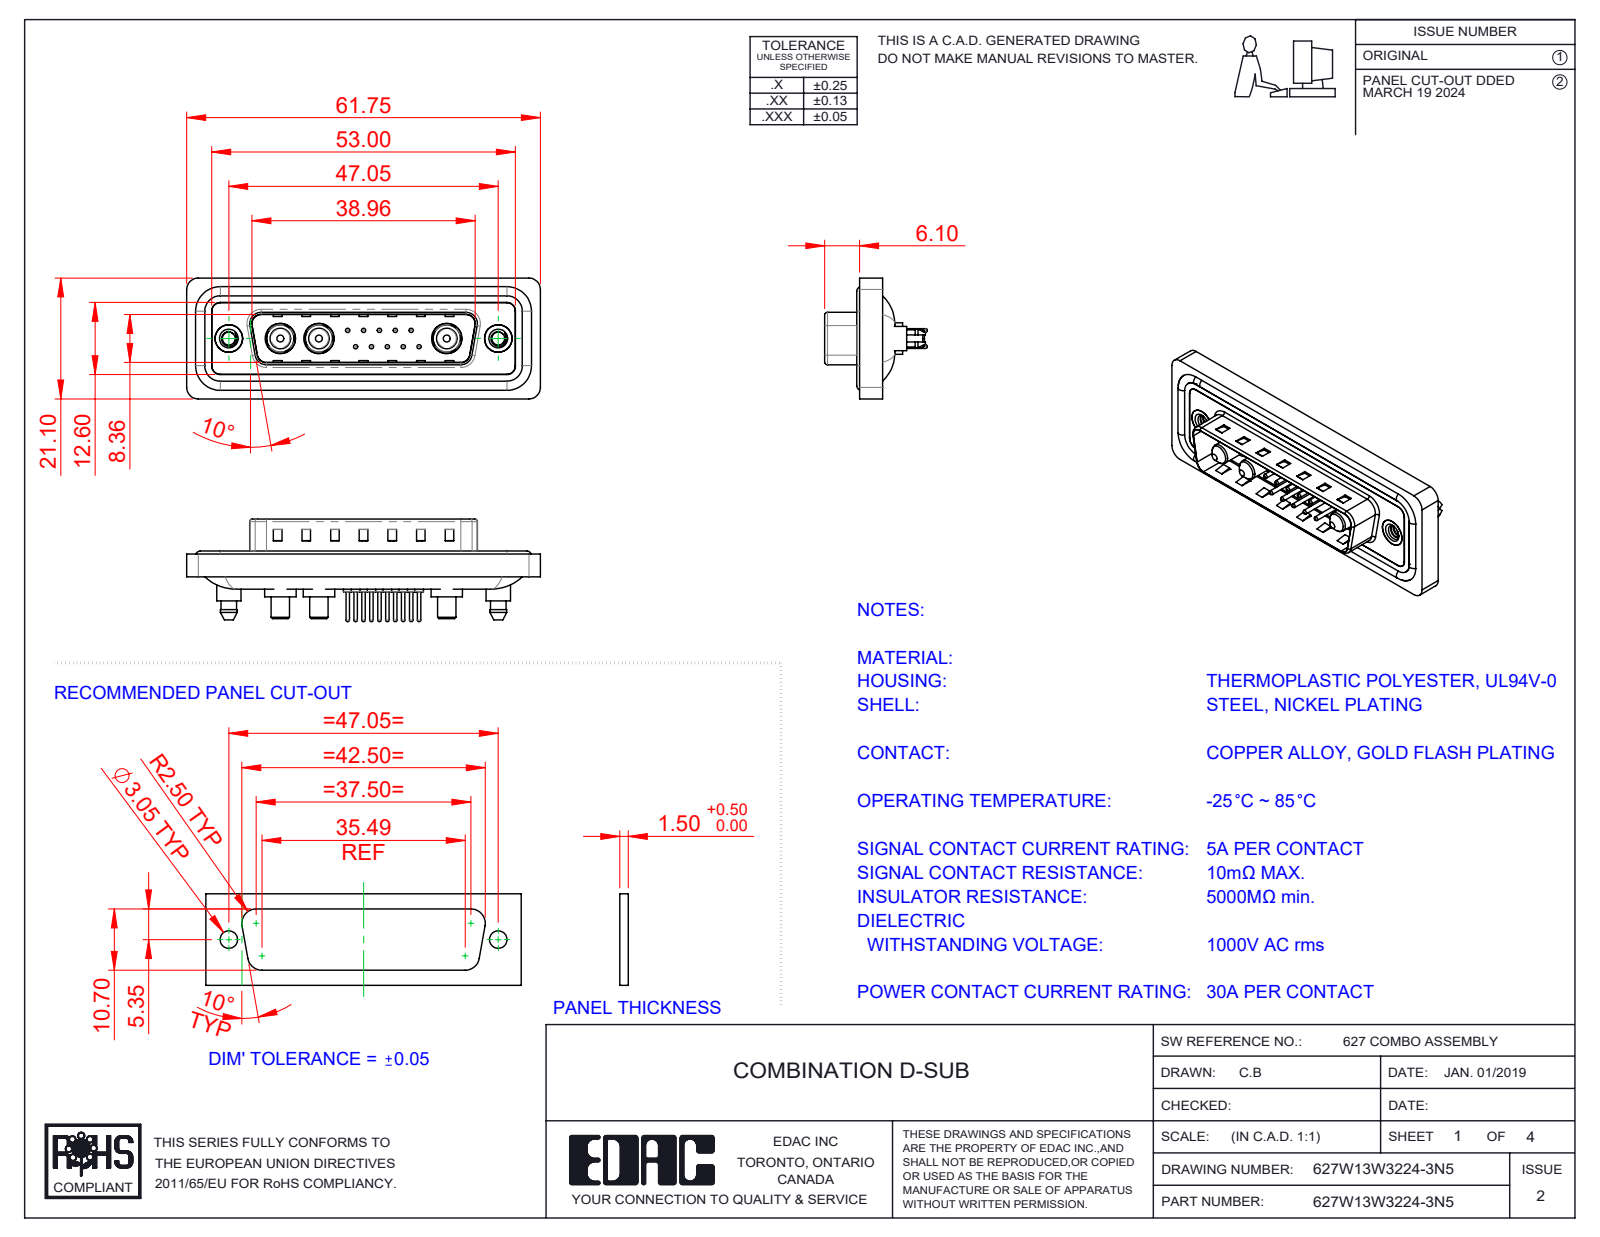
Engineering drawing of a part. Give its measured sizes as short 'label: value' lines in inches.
name: 627Combo Contact Row 2_24; 627Combo Contact Row 1_24; 627Combo Shell Rear_25 Contacts; 627Combo Waterproof Housing_25 Contacts (+5 more)
written by: SolidWorks 2023 (CONFIG_CONTROL_DESIGN)
unit: in
bodies: 23 solids, 1020 faces (325 planar, 417 cylindrical, 278 other)
size: 2.431 × 0.831 × 0.705
volume: 0.457 in³; area: 18.94 in²
holes: 10× ⌀0.03, 10× ⌀0.063, 10× ⌀0.079, 3× ⌀0.191, 3× ⌀0.209, 2× ⌀0.089, 2× ⌀0.157, 2× ⌀0.189, 2× ⌀0.197
bosses: 10× ⌀0.059, 10× ⌀0.024, 4× ⌀0.063, 3× ⌀0.217, 3× ⌀0.205, 3× ⌀0.187, 3× ⌀0.148, 3× ⌀0.142
rounds: 24× R0.059, 18× R0.079, 10× R0.063, 8× R0.02, 4× R0.01, 4× R0.024, 4× R0.026, 4× R0.035
face distances: 0.016, 0.059, 0.043, 0.063, 0.02, 0.122, 0.114, 0.032, 0.377, 0.161
hole spacings: 0.124, 0.109, 0.198, 0.218, 0.295, 0.198, 0.327, 0.398
